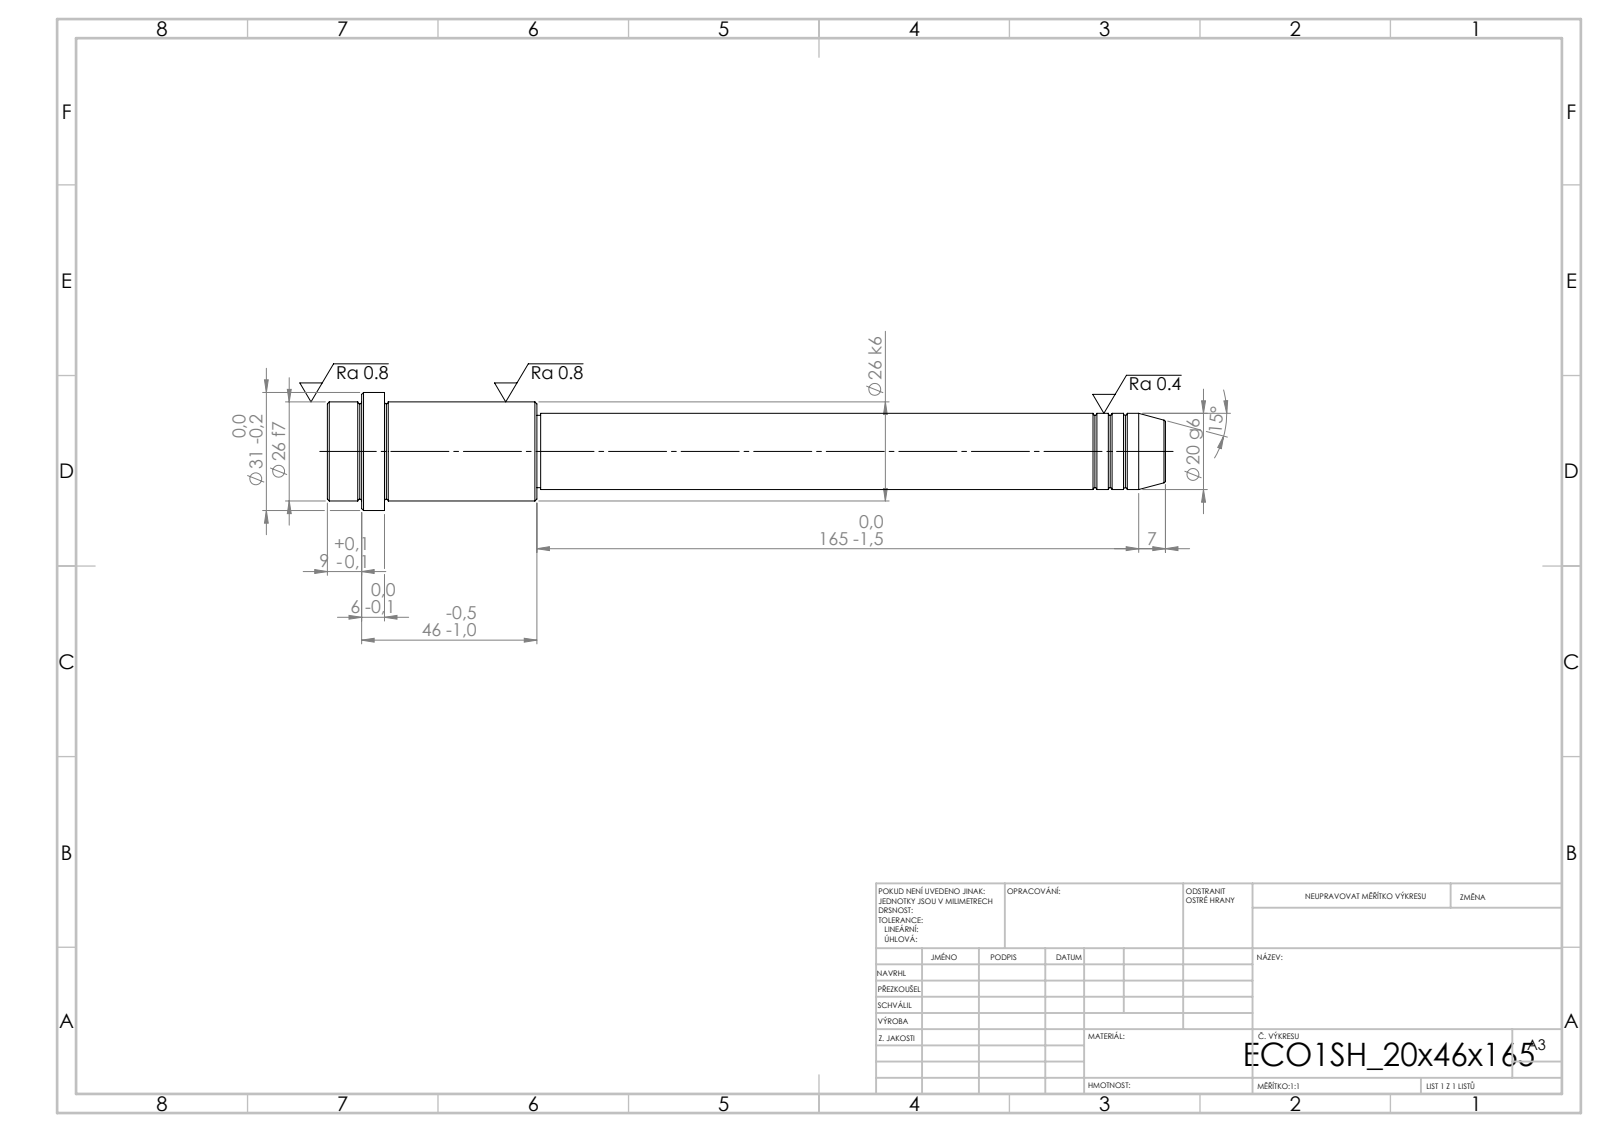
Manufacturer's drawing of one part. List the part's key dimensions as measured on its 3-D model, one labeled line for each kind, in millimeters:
STEP written by: SolidWorks 2019 (CONFIG_CONTROL_DESIGN)
Units: millimetres
Bodies: 1 solid, 52 faces (6 planar, 16 cylindrical, 30 other)
Overall size (bounding box): 220 × 31 × 31
Volume: 81 794 mm³ · Surface area: 16 490 mm²
Round bosses / shafts (diameter × count): ⌀31 ×1, ⌀26 ×1, ⌀20 ×1, ⌀19 ×1
Main face-to-face distances: 15, 40, 55, 165, 205, 220, 211, 46, 6, 9
